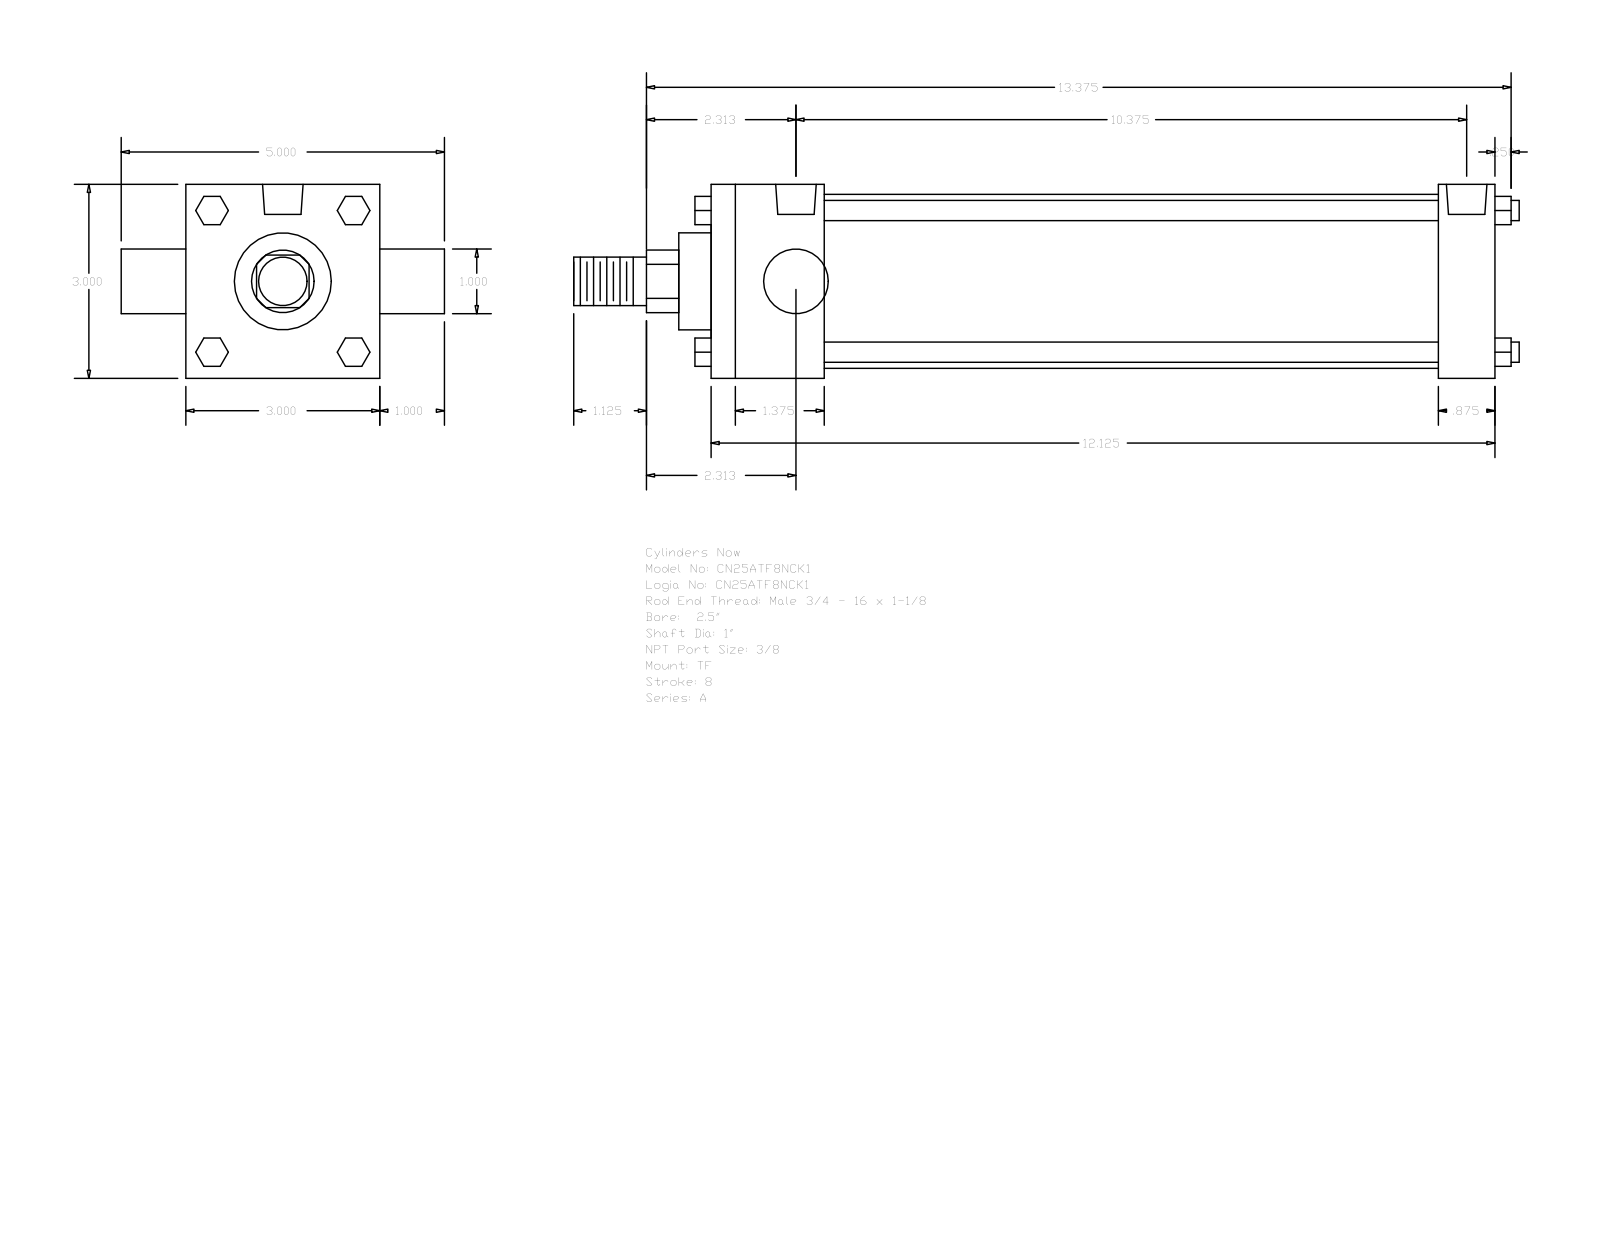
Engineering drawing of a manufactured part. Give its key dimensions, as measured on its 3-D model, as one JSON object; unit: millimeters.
{"part_name": "A_TF__0250_1", "step_written_by": "GSSL Pune (CONFIG_CONTROL_DESIGN)", "units": "millimeters", "bodies": {"solids": 0, "faces": 120, "planar": 92, "cylindrical": 28, "other": 0}, "overall_size": [371.48, 127, 76.2], "round_holes": [[5.56, 3], [15.93, 2]], "round_bosses_or_shafts": [[7.94, 4], [25.4, 2], [68.33, 1], [38.1, 1], [19.05, 1]], "partial_cylinders_radius": [[12.29, 1]], "face_to_face_distances": [76.2, 307.98, 44.45, 285.75, 241.3, 263.53, 22.23, 25.4, 101.6, 320.68], "hole_center_spacings": [2.38, 265.9, 263.52, 268.28]}
